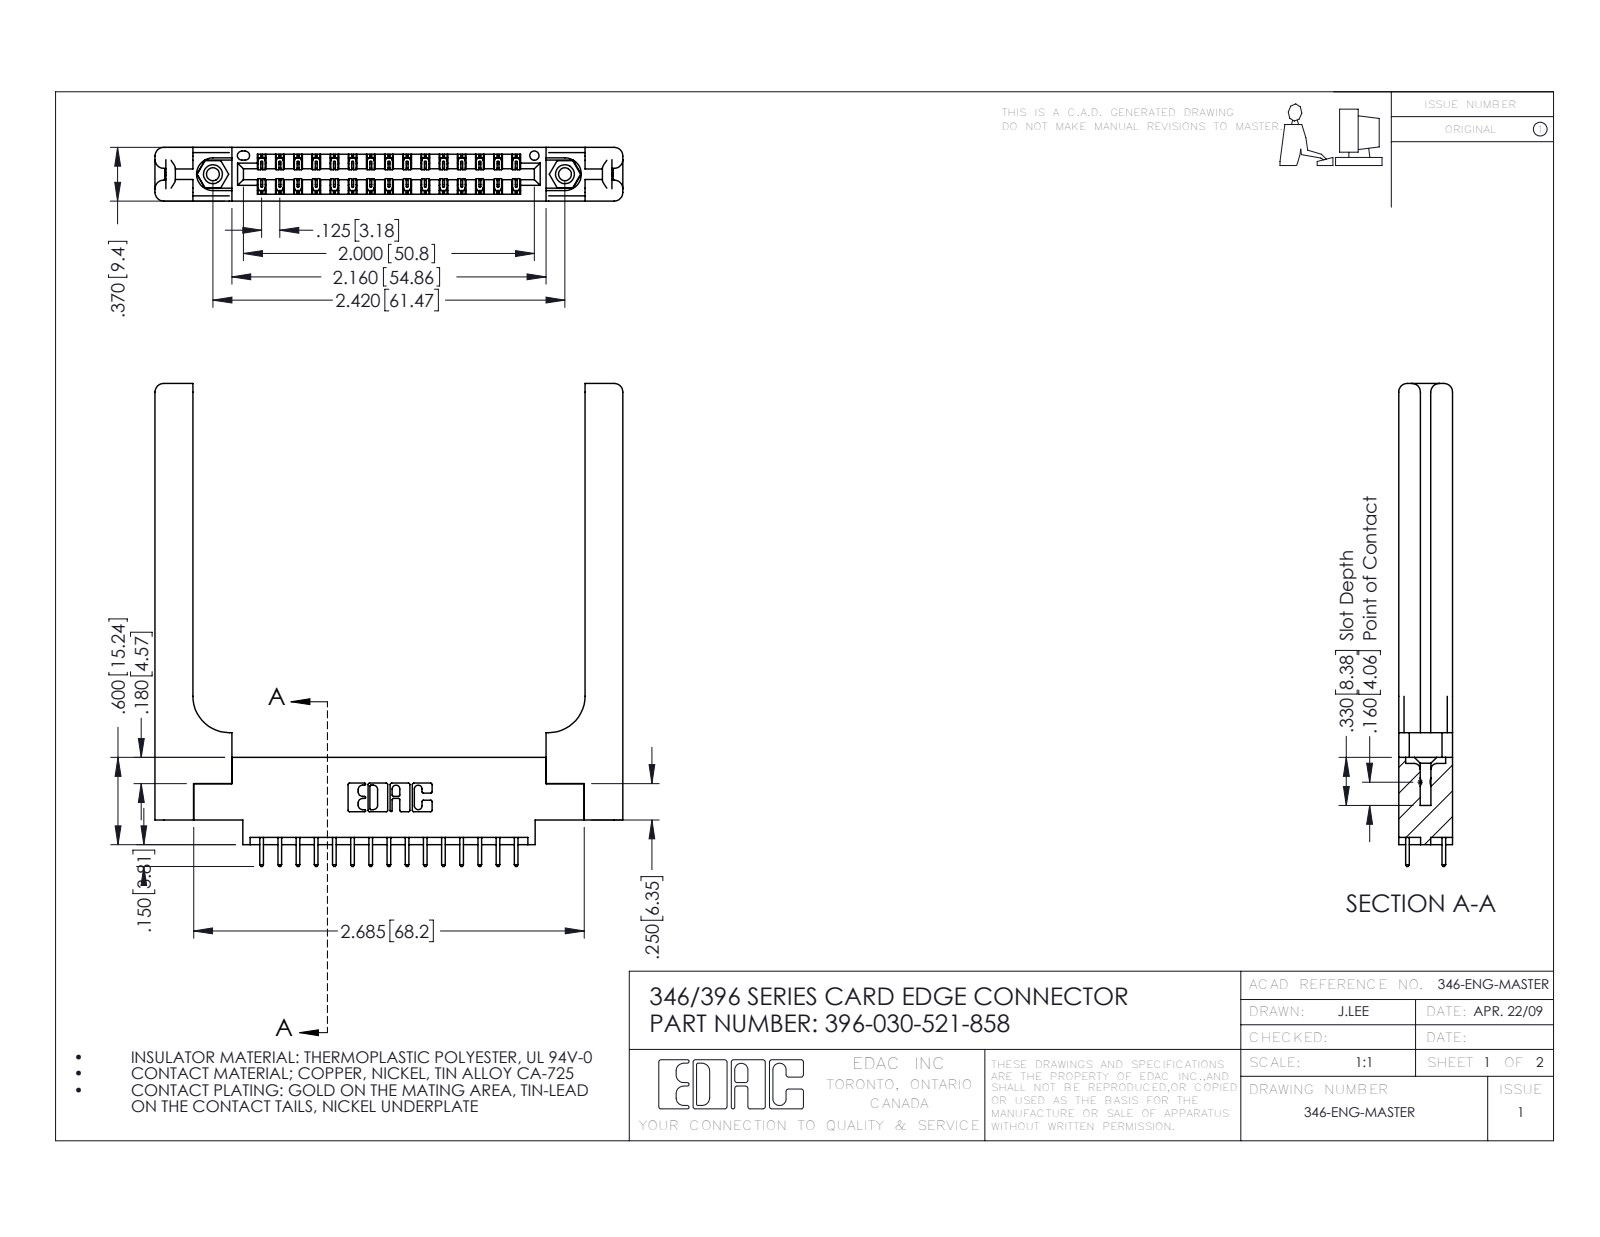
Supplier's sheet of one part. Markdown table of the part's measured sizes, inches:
| quantity | value |
| --- | --- |
| part name | 346-220-058_345-220-058; 396-030-521-858; 346 Part_0.170 Offset - 0.156 Dia-TH; 345-250-001_345-250-001-102 (+1 more) |
| STEP written by | SolidWorks 2016 (CONFIG_CONTROL_DESIGN) |
| units | inches |
| bodies | 35 solids, 1942 faces (1278 planar, 604 cylindrical, 60 other) |
| overall size | 3.32 × 3.216 × 0.37 |
| volume | 0.92 in³ |
| surface area | 23.37 in² |
| round holes (diameter × count) | 0.089 × 2, 0.125 × 2, 0.156 × 2, 0.064 × 1 |
| round bosses / shafts (diameter × count) | 0.155 × 2 |
| partial cylindrical surfaces (radius × count) | 0.006 × 45, 0.01 × 30, 0.01 × 22, 0.06 × 16, 0.007 × 6, 0.031 × 6, 0.026 × 3, 0.014 × 2 |
| main face-to-face distances | 0.37, 0.15, 0.072, 0.148, 0.048, 0.322, 0.25, 0.102, 0.22, 0.173 |
| hole center spacings | 0.246, 2.213, 2.42 |
